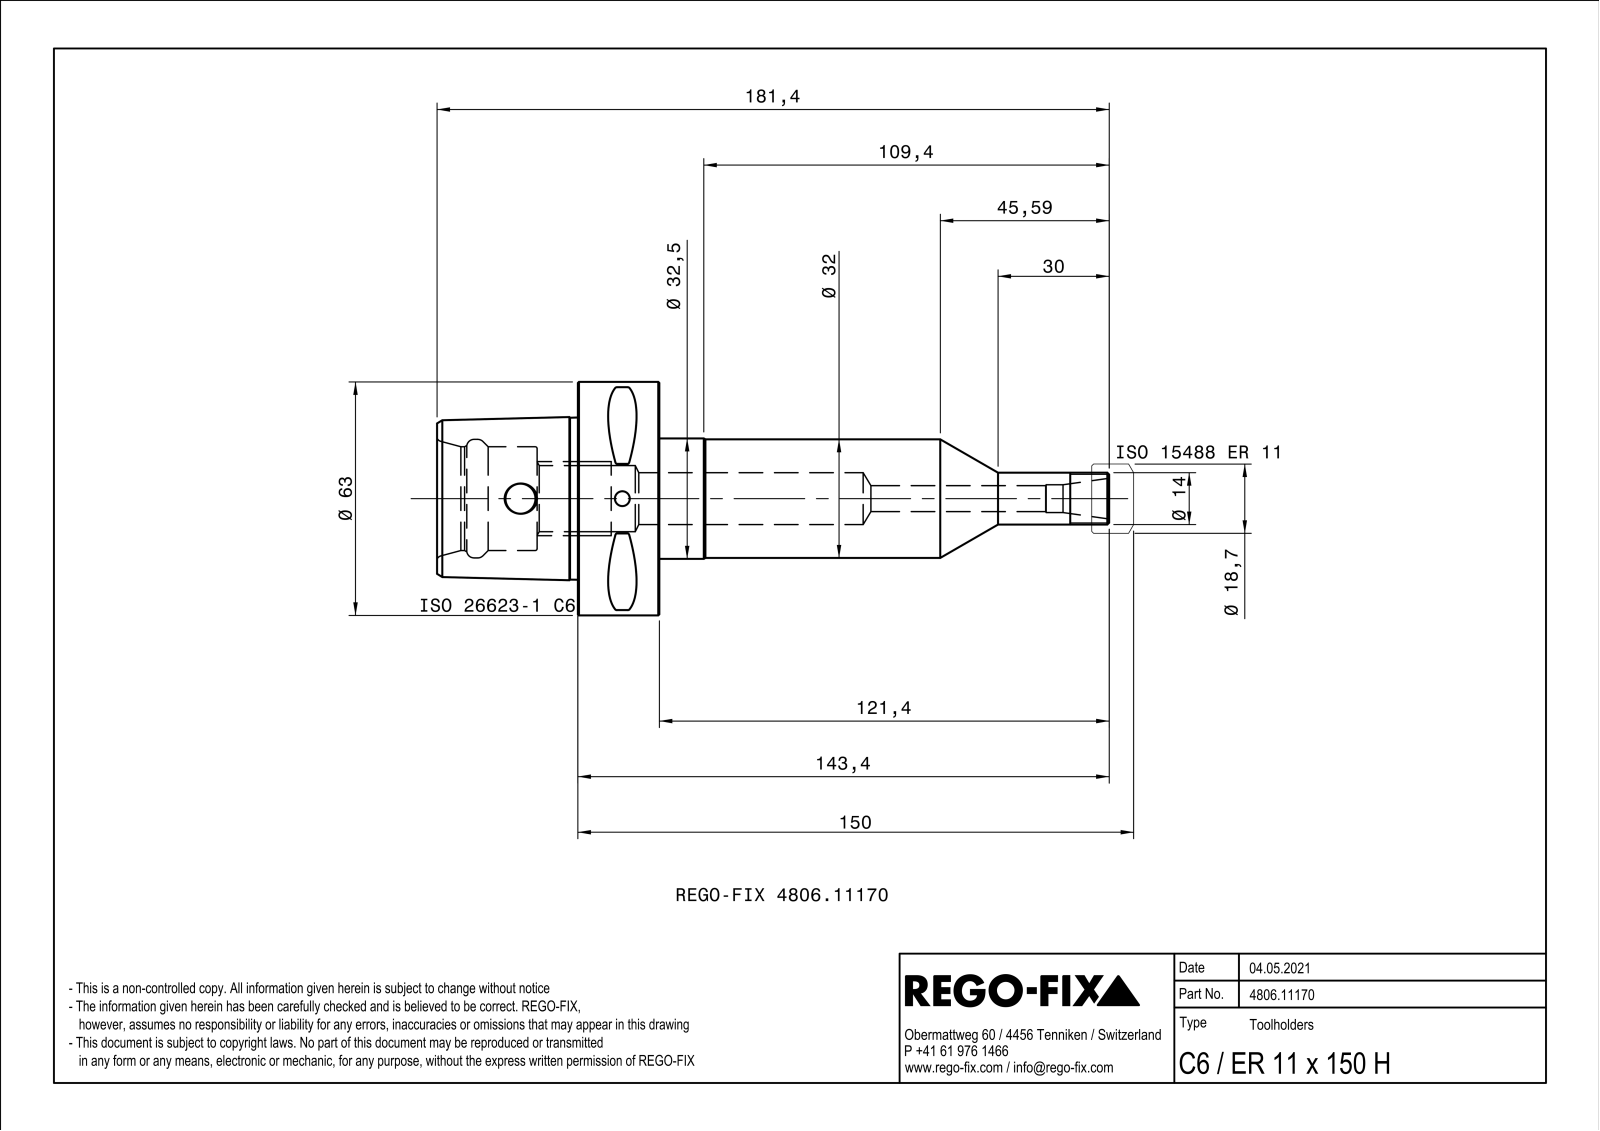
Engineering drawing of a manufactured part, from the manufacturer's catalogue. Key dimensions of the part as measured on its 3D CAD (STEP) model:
Part name (STEP PRODUCT): NOCUT
STEP written by: SIEMENS PLM Software Solid Edge ST10 (AUTOMOTIVE_DESIGN)
Units: millimetres
Bodies: 1 solid, 124 faces (20 planar, 27 cylindrical, 77 other)
Overall size (bounding box): 181.4 × 63 × 63
Volume: 156 208 mm³ · Surface area: 33 661 mm²
Round holes (diameter × count): ⌀4 ×1, ⌀7 ×1, ⌀7.5 ×1, ⌀8.1 ×1, ⌀17.84 ×1, ⌀28 ×1, ⌀32 ×1
Round bosses / shafts (diameter × count): ⌀63 ×1, ⌀32.5 ×1, ⌀14 ×1
Partial cylindrical surfaces — rounded edges, fillets, slot ends (radius × count): R0.5 ×8, R5 ×1
Main face-to-face distances: 22, 60, 38, 24.89, 33, 11, 27, 55.8, 22.1, 10.9
Hole centre spacings: 27.5
